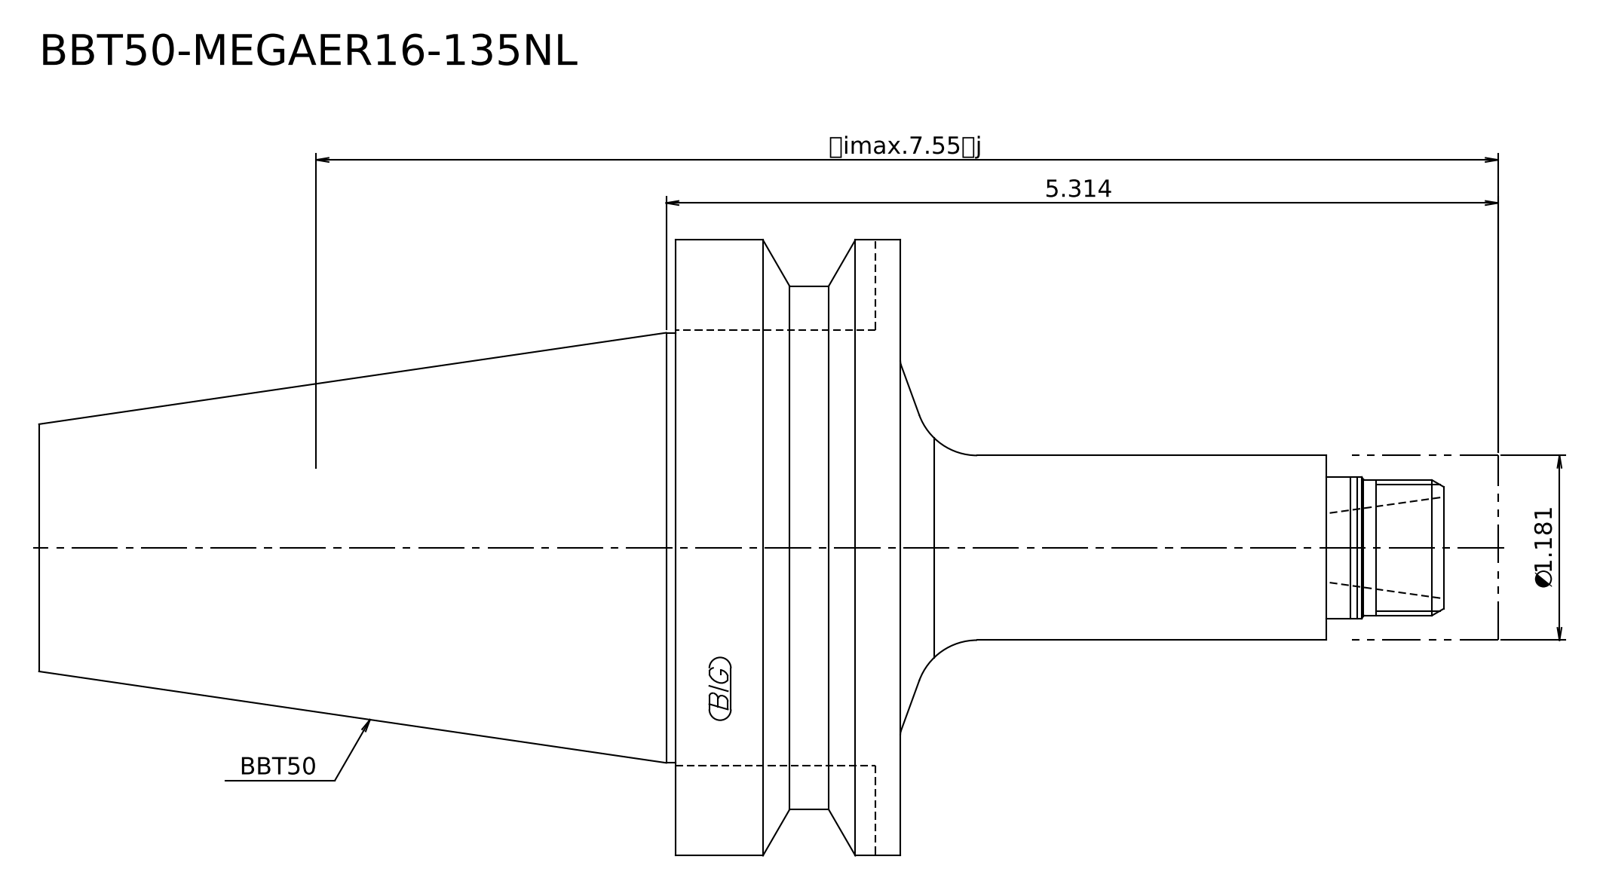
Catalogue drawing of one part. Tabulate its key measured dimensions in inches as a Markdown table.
| quantity | value |
| --- | --- |
| STEP written by | Kubotek KeyCreator 2011 V10.0.2 (22737) (automotive_design) |
| units | inches |
| bodies | 2 solids, 21 faces (7 planar, 8 cylindrical, 6 other) |
| overall size | 9.323 × 3.937 × 3.937 |
| volume | 36.78 in³ |
| surface area | 86.38 in² |
| round bosses / shafts (diameter × count) | 3.937 × 1, 3.346 × 1, 2.75 × 1, 1.181 × 1, 0.906 × 1, 0.866 × 1 |
| main face-to-face distances | 1.437, 5.504, 4.067, 2.835, 4.272, 8.339, 0.984, 3.819, 5.256, 9.323 |
